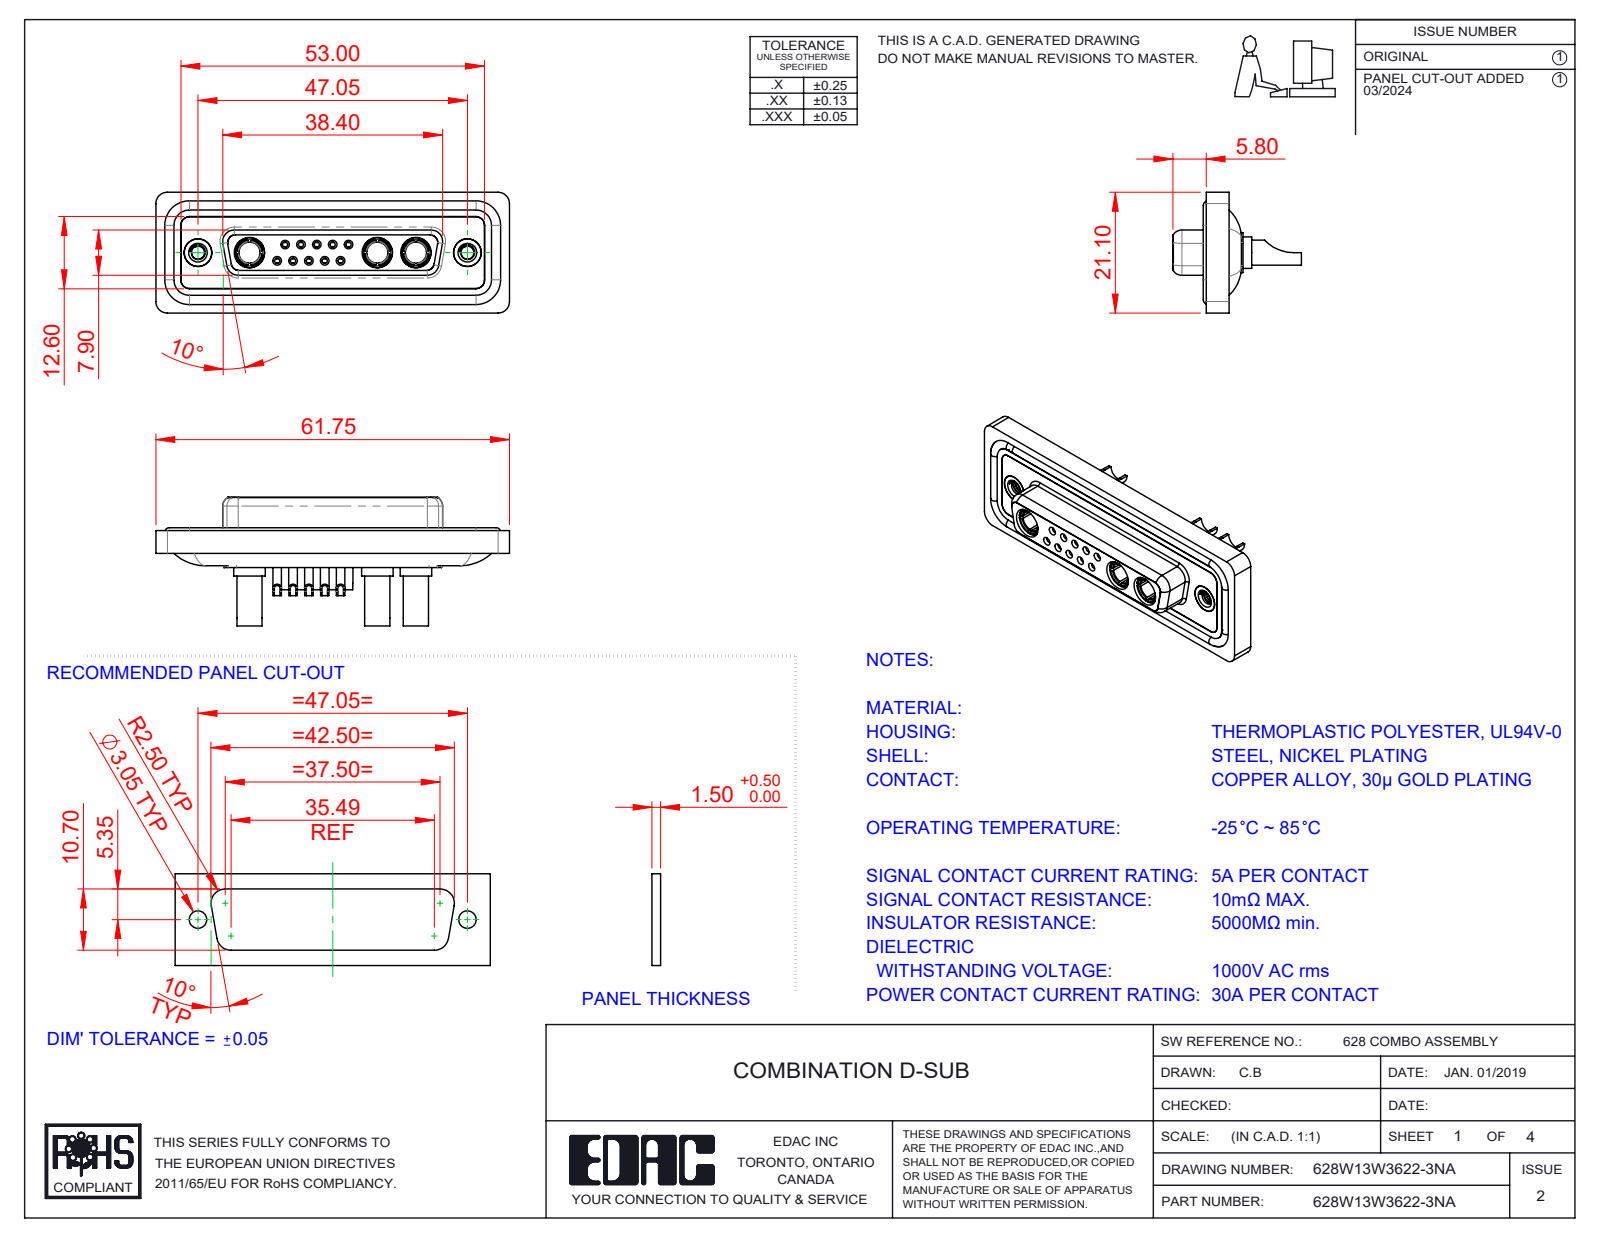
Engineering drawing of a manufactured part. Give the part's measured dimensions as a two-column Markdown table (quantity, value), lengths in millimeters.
| quantity | value |
| --- | --- |
| part name | 628Combo Threaded Rivet_A; 628Combo Contact Row 1_22; 628Combo Waterproof Housing_25 Contacts; Power Socket_30A SC (+5 more) |
| STEP written by | SolidWorks 2023 (CONFIG_CONTROL_DESIGN) |
| units | millimeters |
| bodies | 23 solids, 1174 faces (371 planar, 478 cylindrical, 325 other) |
| overall size | 61.75 × 22.45 × 21.1 |
| volume | 8 367 mm³ |
| surface area | 14 134 mm² |
| round holes (diameter × count) | 0.9 × 10, 1 × 10, 1.1 × 10, 1.5 × 10, 2 × 10, 1.6 × 5, 1.7 × 5, 4.85 × 5, 3.5 × 3, 3.7 × 3, 5.3 × 3, 2.26 × 2 |
| round bosses / shafts (diameter × count) | 2.2 × 10, 1.6 × 9, 5.5 × 3, 5.2 × 3, 4.96 × 3, 4.75 × 3, 4.4 × 3, 3.75 × 3 |
| partial cylindrical surfaces (radius × count) | 1.5 × 22, 2 × 18, 1.35 × 8, 1.6 × 8, 1 × 6, 0.25 × 4, 0.5 × 4, 0.6 × 4 |
| main face-to-face distances | 0.4, 1.8, 7.45, 5.65, 0.5, 6.6, 7.05, 1.6, 2.9, 1.1 |
| hole center spacings | 3.16, 2.77, 5.03, 5.04, 5.54, 8.31, 7.49, 2.76 |
